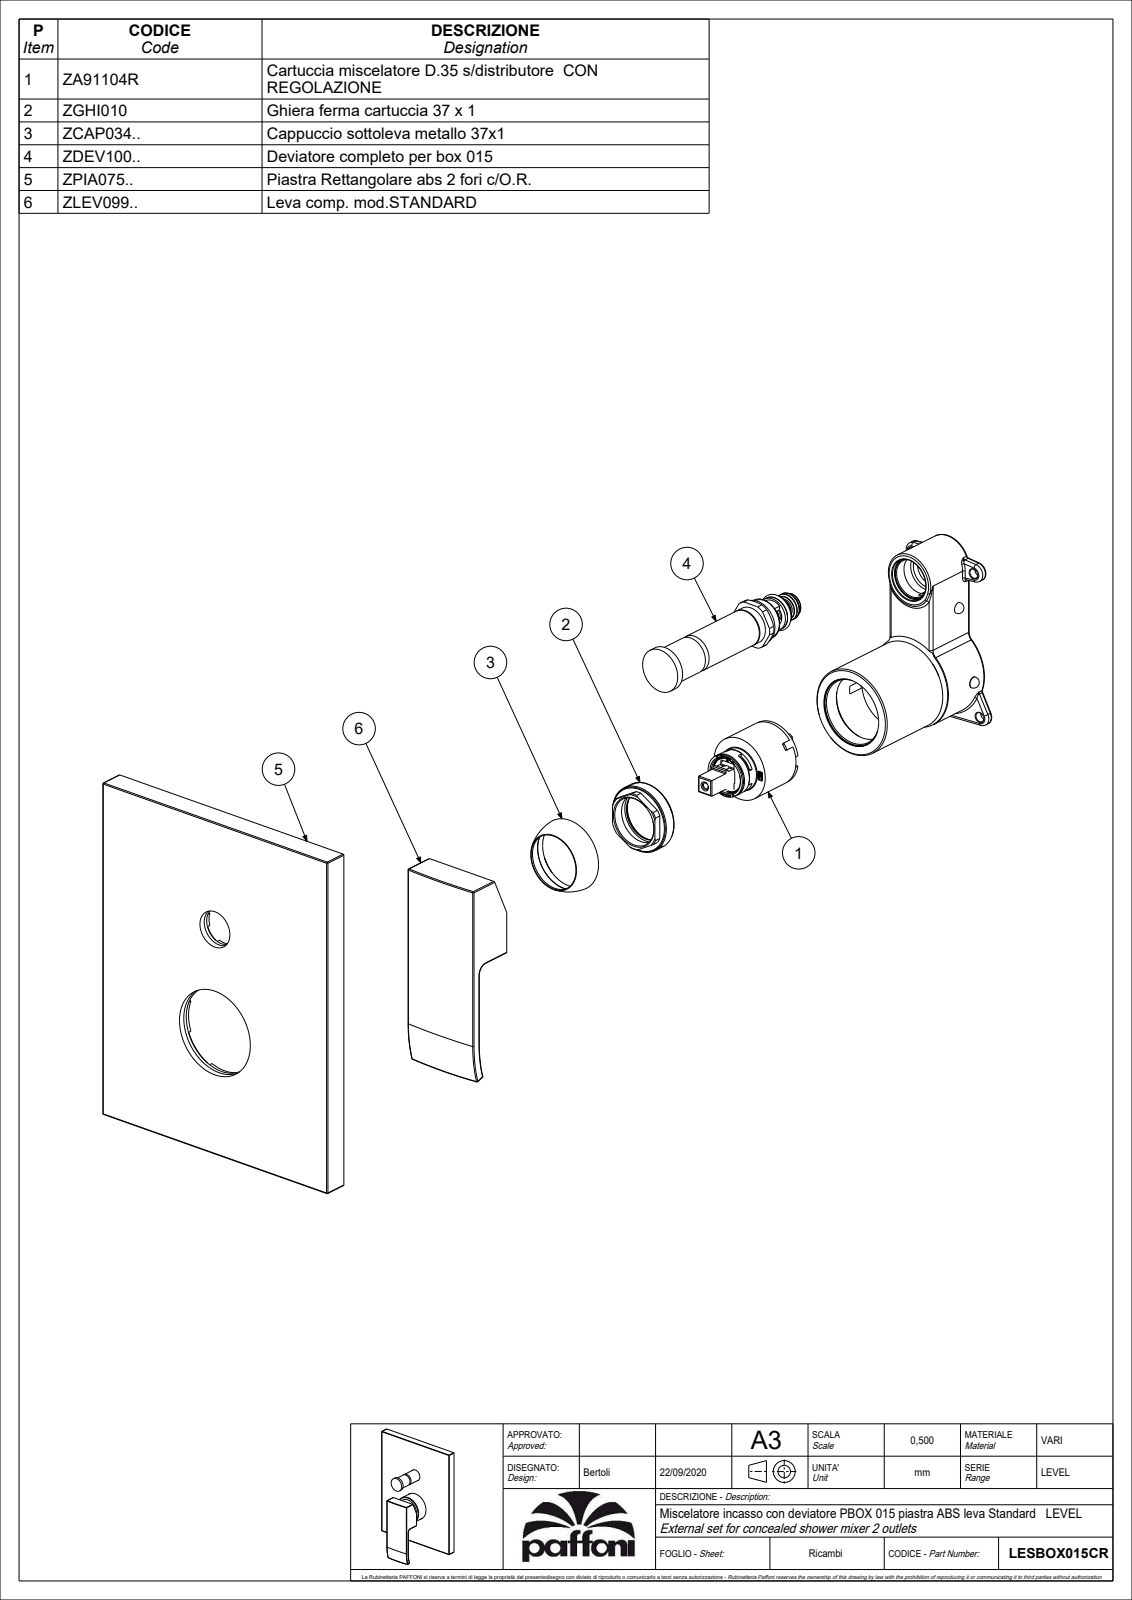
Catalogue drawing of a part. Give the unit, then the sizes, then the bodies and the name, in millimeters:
Units: millimetres
Overall size (bounding box): 210.82 × 154 × 65.21
Round holes (diameter × count): ⌀5 ×3, ⌀7 ×3, ⌀2 ×2, ⌀4 ×2, ⌀3 ×1, ⌀5.5 ×1, ⌀7.1 ×1, ⌀7.8 ×1, ⌀16 ×1, ⌀18.2 ×1, ⌀19.5 ×1, ⌀19.9 ×1
Round bosses / shafts (diameter × count): ⌀4.8 ×2, ⌀57 ×1, ⌀48.1 ×1, ⌀39 ×1, ⌀35 ×1, ⌀34.8 ×1, ⌀32.2 ×1, ⌀29 ×1
Partial cylindrical surfaces — rounded edges, fillets, slot ends (radius × count): R0.5 ×41, R1.5 ×14, R0.15 ×11, R0.3 ×4, R2 ×4, R1 ×2, R300 ×2, R2.25 ×1
Main face-to-face distances: 13.5, 10, 3.5, 23.5, 54.5, 31, 130.5, 76, 99.5, 154
Hole centre spacings: 8.6, 13.45, 15.13, 21.93, 50.8, 65.38, 8, 14
Volume: 338 901 mm³ · Surface area: 131 230 mm²
Bodies: 5 solids, 1104 faces (649 planar, 287 cylindrical, 168 other)
Part name (STEP PRODUCT): LESBOX015CR
STEP written by: CREO PARAMETRIC BY PTC INC, 2020044 (CONFIG_CONTROL_DESIGN)
